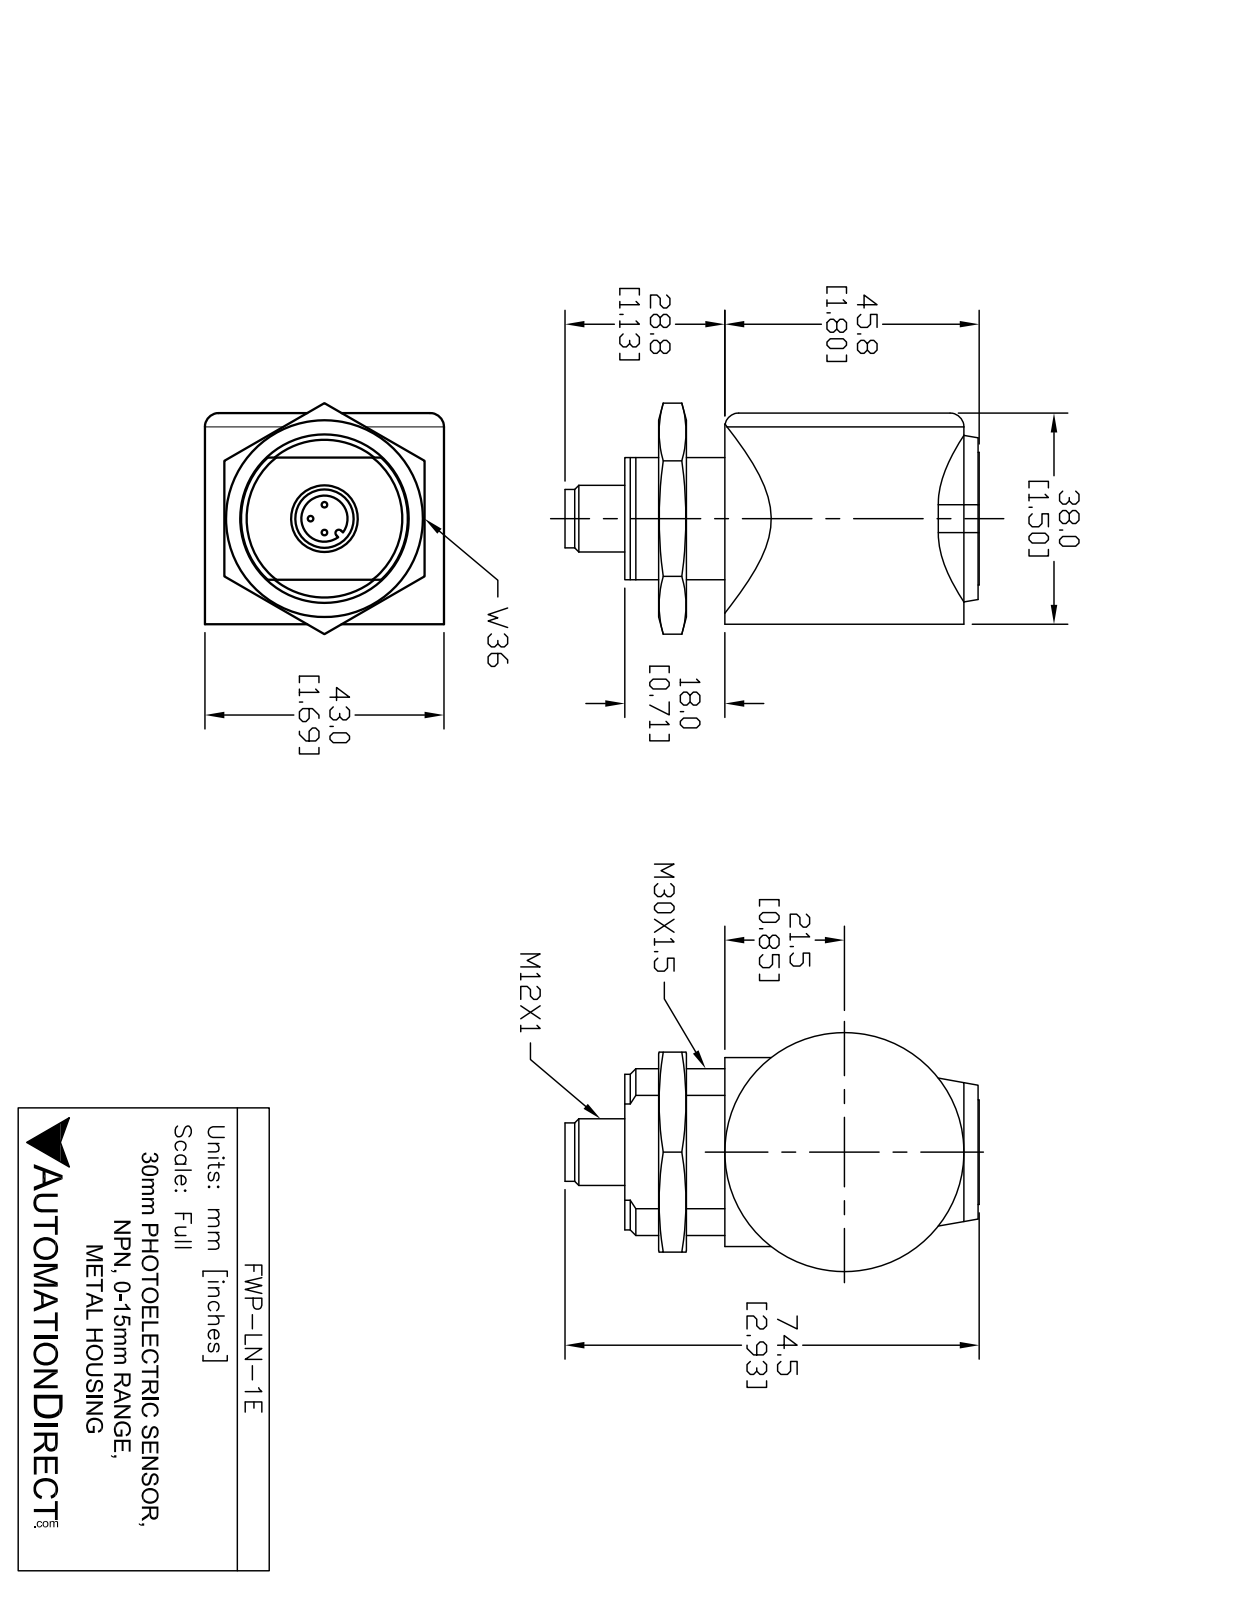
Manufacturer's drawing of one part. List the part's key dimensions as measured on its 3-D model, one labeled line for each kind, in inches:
Part name (STEP PRODUCT): FWP-LN-1E
STEP written by: SolidWorks 2013 (AUTOMOTIVE_DESIGN)
Units: inches
Bodies: 1 solid, 60 faces (29 planar, 24 cylindrical, 7 other)
Overall size (bounding box): 2.928 × 1.69 × 1.49
Volume: 4.417 in³ · Surface area: 19.34 in²
Round holes (diameter × count): ⌀0.315 ×1
Round bosses / shafts (diameter × count): ⌀0.04 ×3, ⌀1.69 ×1, ⌀0.47 ×1, ⌀0.39 ×1
Partial cylindrical surfaces — rounded edges, fillets, slot ends (radius × count): R0.64 ×2, R0.025 ×1, R0.545 ×1, R0.587 ×1
Main face-to-face distances: 1.49, 2.518, 0.11, 2.408, 0.3, 0.19, 2.218, 1.178, 0.312, 0.312
